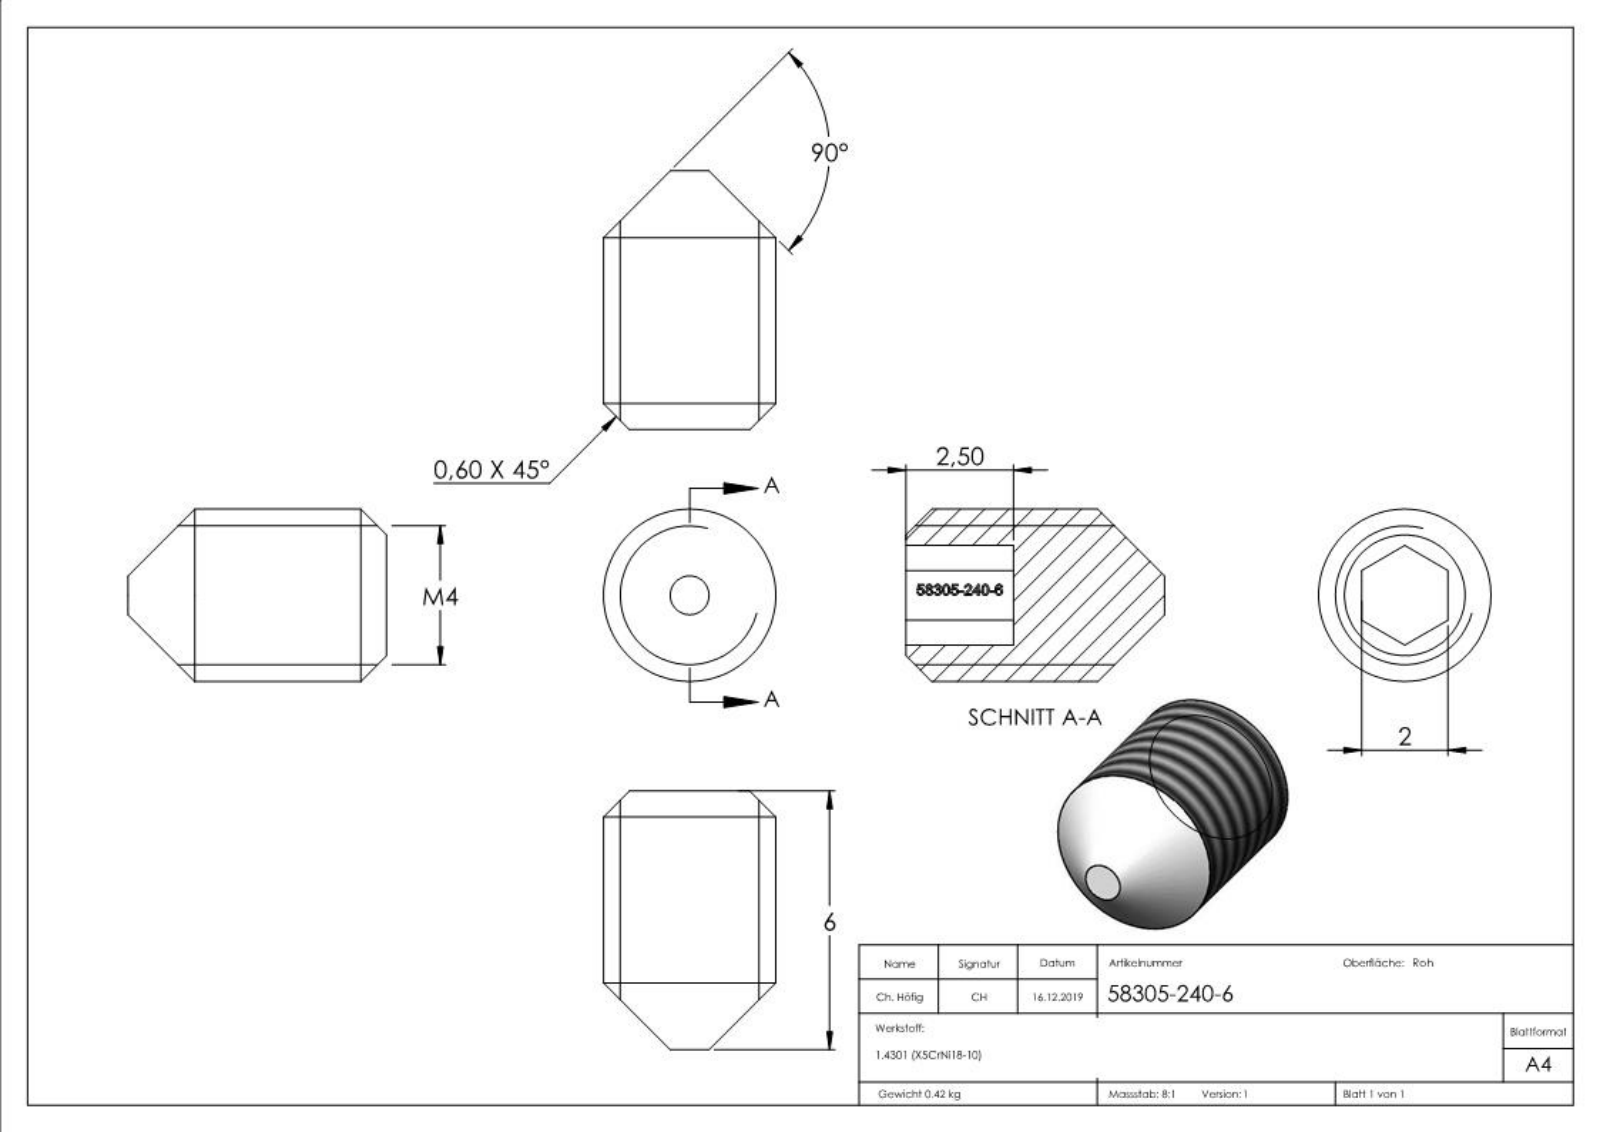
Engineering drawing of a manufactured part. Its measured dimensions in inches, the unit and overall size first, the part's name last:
Units: inches
Overall size (bounding box): 2.756 × 0.157 × 0.157
Round bosses / shafts (diameter × count): ⌀0.157 ×1
Main face-to-face distances: 0.079, 0.098, 0.138, 0.236, 0.083, 0.032, 0.17, 0.067, 0.03, 0.171
Volume: 0.003 in³ · Surface area: 0.155 in²
Bodies: 1 solid, 165 faces (70 planar, 1 cylindrical, 94 other)
Part name (STEP PRODUCT): 58305-240-6
STEP written by: SolidWorks 2015 (CONFIG_CONTROL_DESIGN)
